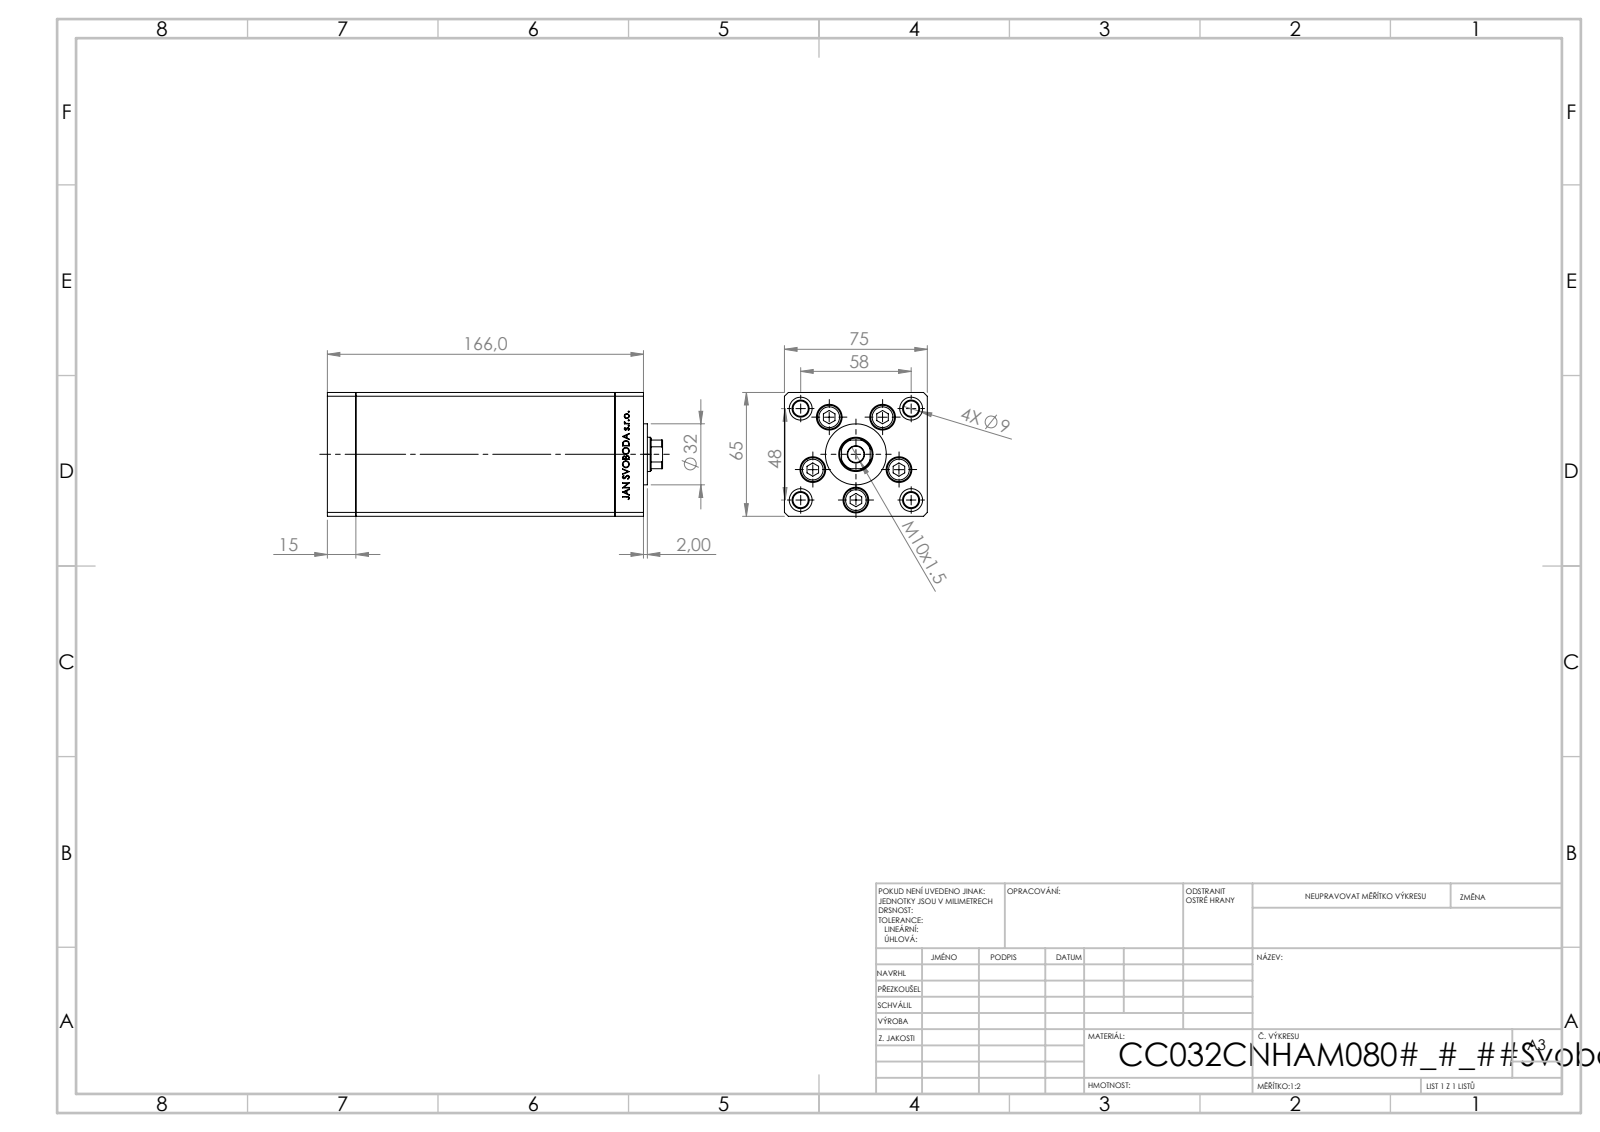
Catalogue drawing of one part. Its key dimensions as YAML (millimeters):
part_name: "V220C FRONT; V220C_C MIDDLE; V220C BACK_C; V220C_VC_C (+1 more)"
step_written_by: "SolidWorks 2019 (CONFIG_CONTROL_DESIGN)"
units: millimeters
bodies: {solids: 13, faces: 1179, planar: 542, cylindrical: 175, other: 462}
overall_size: [176, 75, 65]
volume: 676888
surface_area: 143721
round_holes:
  - {diameter: 9, count: 9}
  - {diameter: 13.5, count: 5}
  - {diameter: 2, count: 4}
  - {diameter: 8, count: 4}
  - {diameter: 12, count: 4}
  - {diameter: 13.16, count: 4}
  - {diameter: 8.5, count: 1}
  - {diameter: 12.5, count: 1}
  - {diameter: 18, count: 1}
round_bosses_or_shafts:
  - {diameter: 8, count: 5}
  - {diameter: 12.5, count: 4}
  - {diameter: 32, count: 1}
partial_cylinders:
  - {radius: 0.93, count: 2}
  - {radius: 8.5, count: 1}
face_to_face_distances: [75, 65, 15, 136, 151, 166, 28, 13, 142, 9]
hole_center_spacings: [24, 37.64, 15.67, 17.22, 27.71, 28.83, 29, 32.63]
